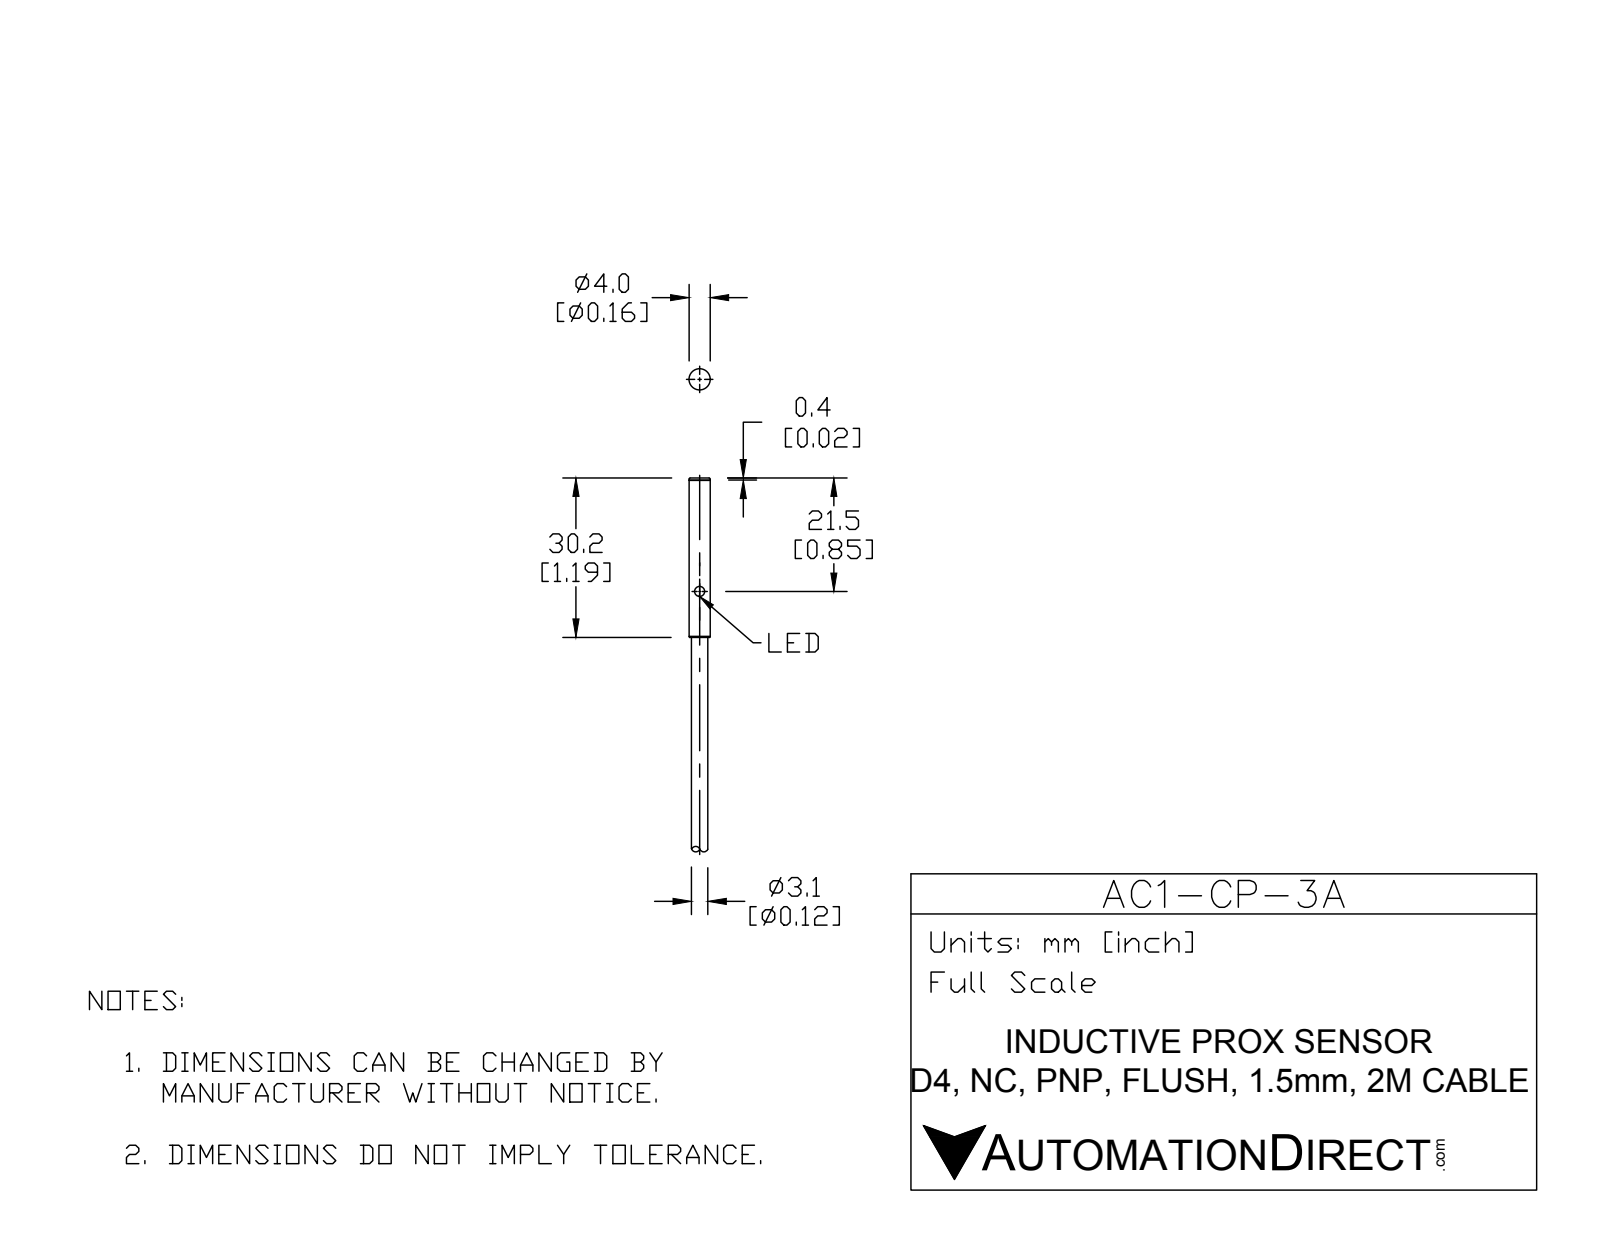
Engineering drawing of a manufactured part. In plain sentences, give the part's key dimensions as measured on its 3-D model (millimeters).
The part is named "AC1-CP-3A". Its 3-D file was written by "SolidWorks 2015 (CONFIG_CONTROL_DESIGN)". It is 2 solids with 20 faces: 6 planar, 8 cylindrical and 6 other. Overall it measures 80.2 by 4 by 4 millimeters. Its volume is 756 cubic millimeters and its surface area 905 square millimeters. Round holes: 1 of diameter 1.9. Round bosses or shafts: 1 of diameter 4, 1 of diameter 3.1. The main face-to-face distances are 30.2, 50, 80.2, 79.8, 29.8, 0.4.
